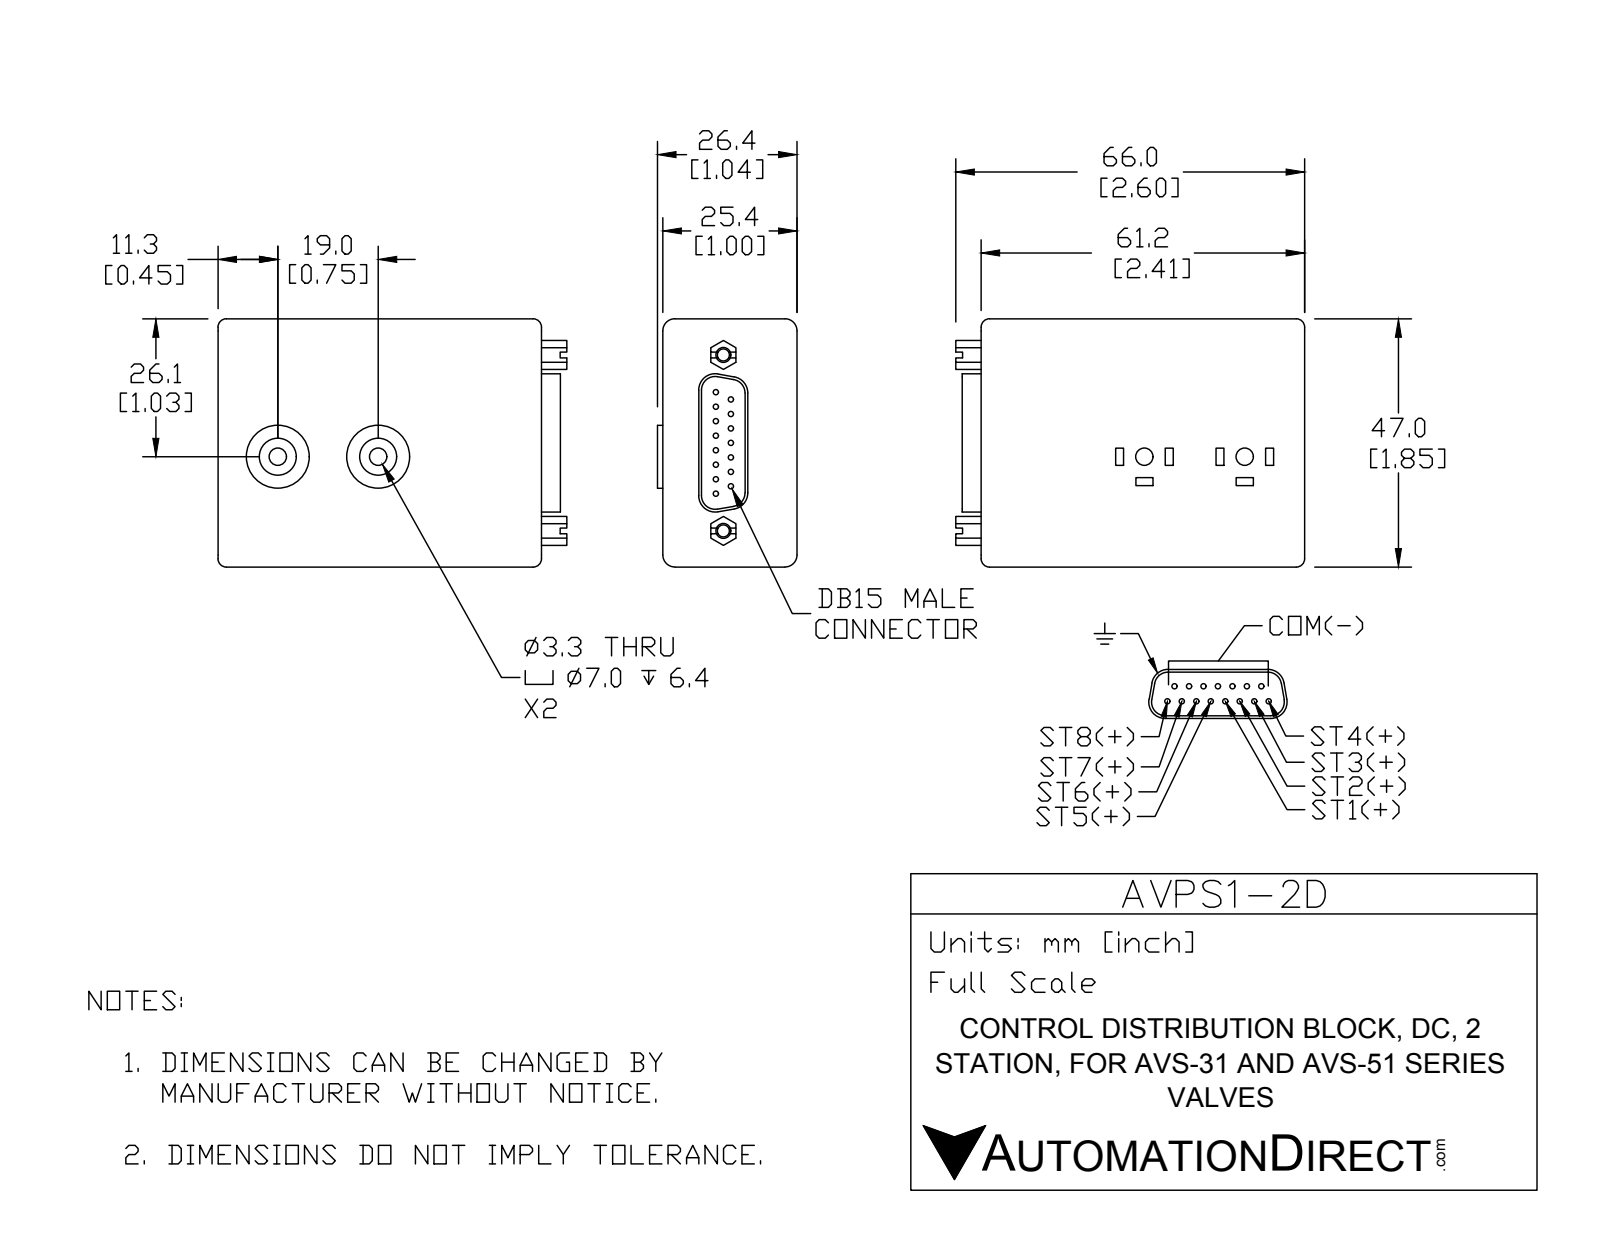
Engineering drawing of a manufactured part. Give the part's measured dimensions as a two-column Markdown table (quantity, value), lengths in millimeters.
| quantity | value |
| --- | --- |
| part name | AVPS1-2D |
| STEP written by | SolidWorks 2016 (AUTOMOTIVE_DESIGN) |
| units | millimeters |
| bodies | 1 solid, 173 faces (93 planar, 68 cylindrical, 12 other) |
| overall size | 66 × 47 × 26.4 |
| volume | 71 600 mm³ |
| surface area | 13 040 mm² |
| round holes (diameter × count) | 2.3 × 2, 3.3 × 2, 7 × 2 |
| round bosses / shafts (diameter × count) | 1 × 15, 11.9 × 2 |
| partial cylindrical surfaces (radius × count) | 1.6 × 8, 2.3 × 4, 2.6 × 4, 3.1 × 4 |
| main face-to-face distances | 25.4, 47, 61.2, 3.1, 58.1, 0.5, 1, 26.4, 8.8, 8.3 |
| hole center spacings | 19, 33.3 |
